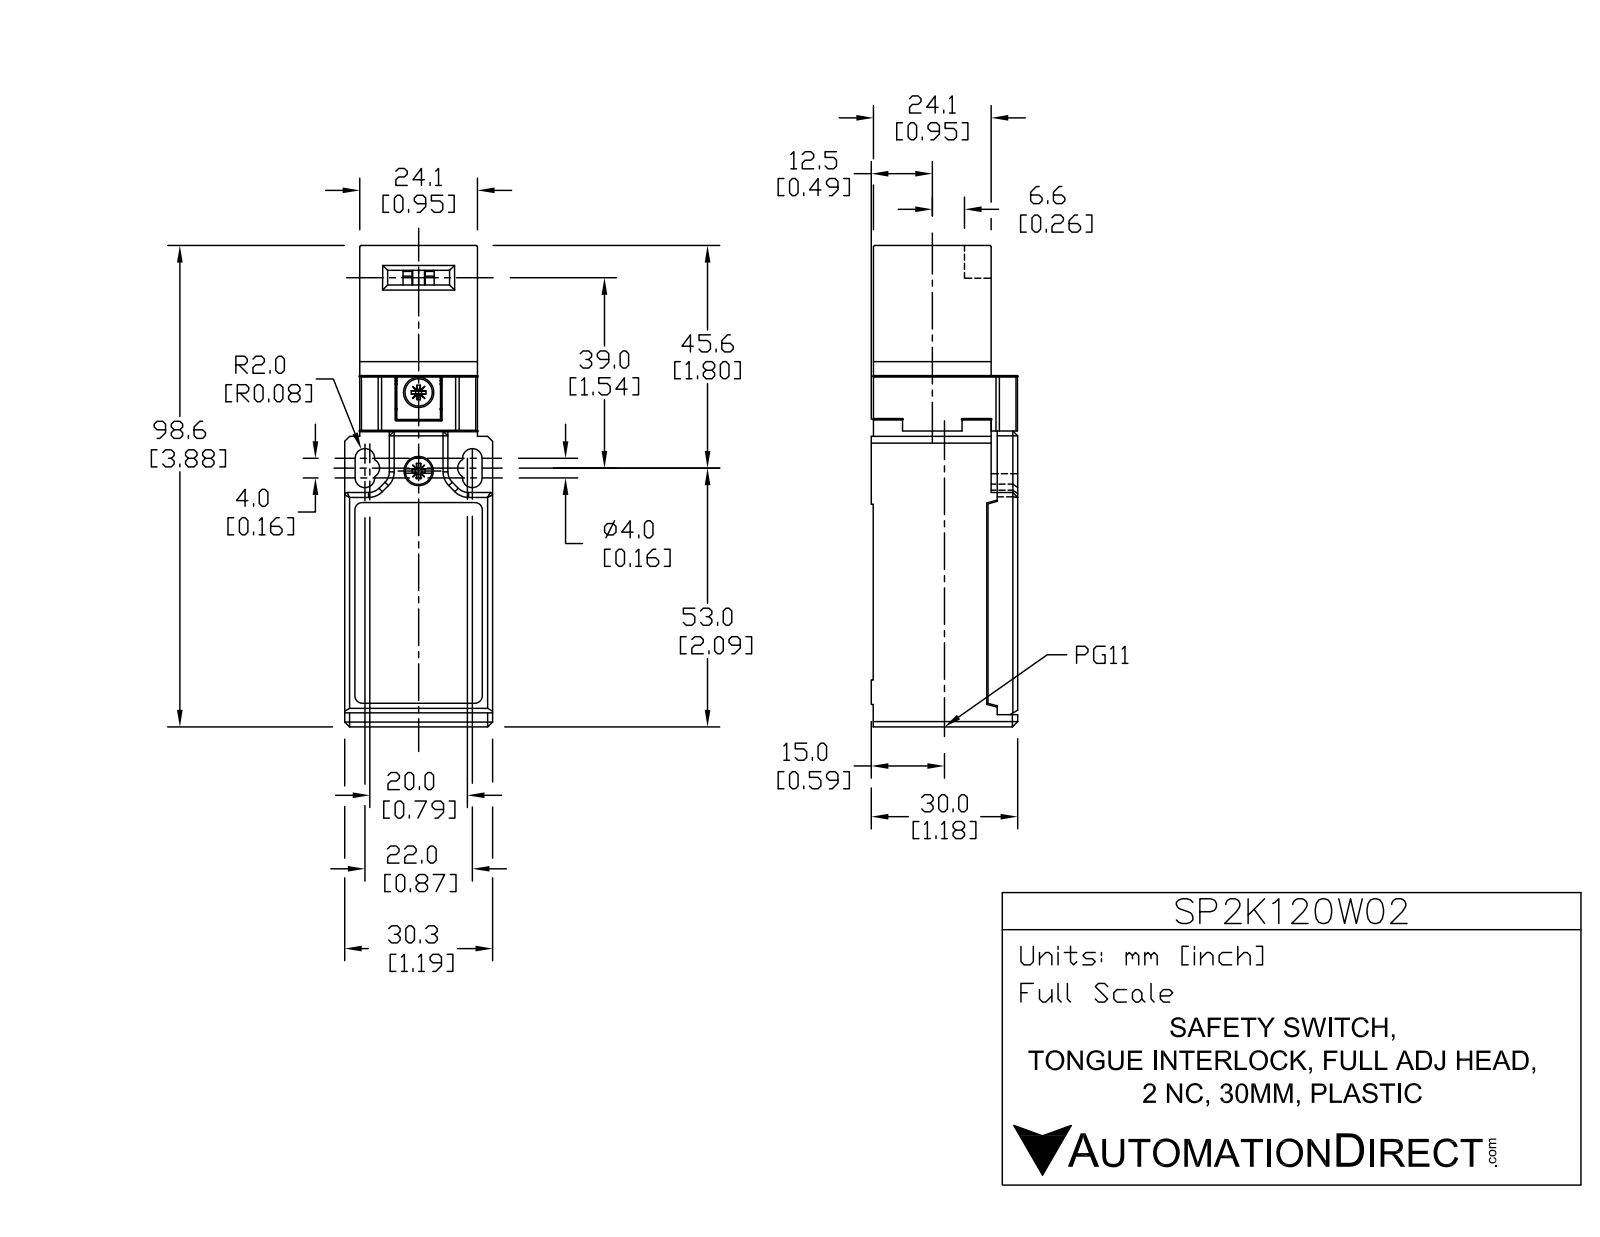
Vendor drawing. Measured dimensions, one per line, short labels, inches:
name: SP2K120W02
written by: SolidWorks 2017 (AUTOMOTIVE_DESIGN)
unit: in
bodies: 3 solids, 160 faces (111 planar, 36 cylindrical, 13 other)
size: 3.902 × 1.204 × 1.193
volume: 4.393 in³; area: 28.76 in²
holes: 1× ⌀0.236, 1× ⌀0.591, 1× ⌀0.669, 1× ⌀0.748
bosses: 1× ⌀0.22
rounds: 6× R0.079, 4× R0.02, 4× R0.118, 1× R0.394, 1× R0.4
face distances: 0.124, 1.069, 0.945, 1.193, 1.165, 0.441, 0.22, 1.181, 2.406, 2.846
hole spacings: 0.083
